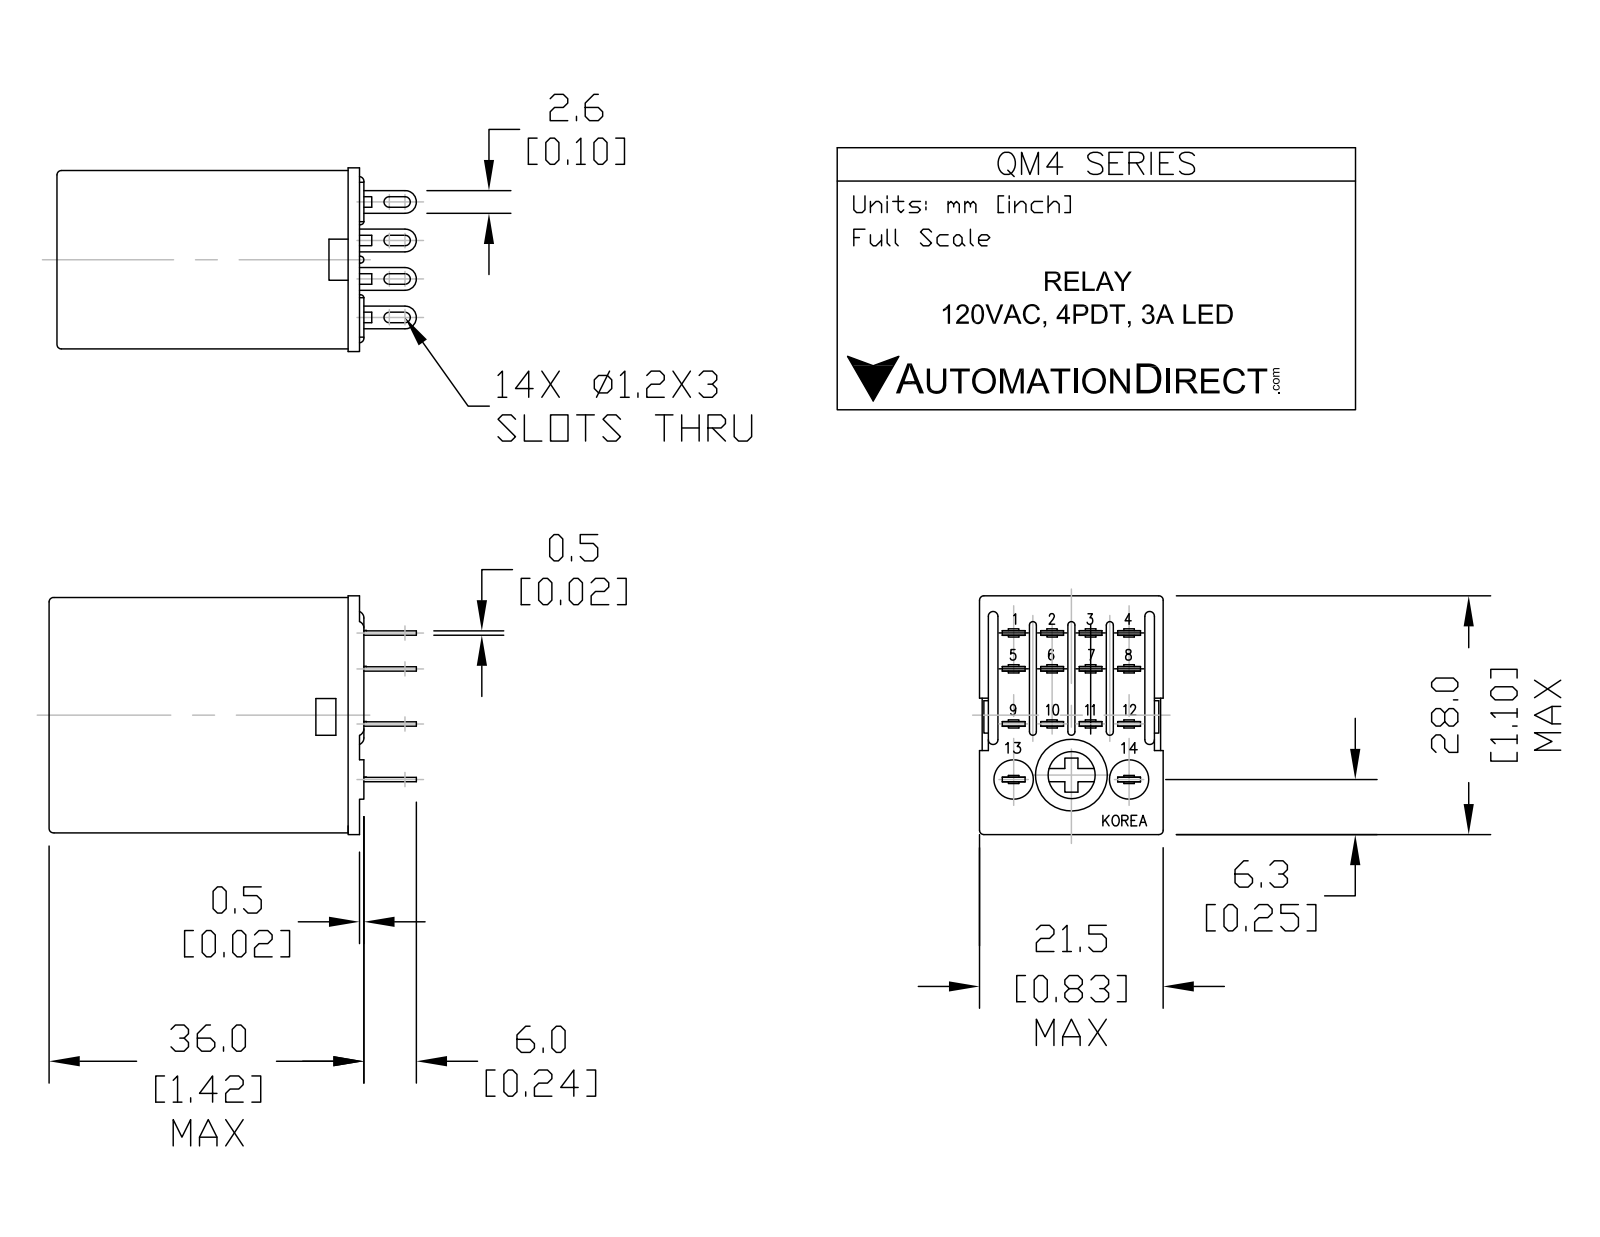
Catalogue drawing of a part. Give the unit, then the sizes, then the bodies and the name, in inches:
Units: inches
Overall size (bounding box): 1.654 × 1.102 × 0.846
Round holes (diameter × count): ⌀0.256 ×1
Round bosses / shafts (diameter × count): ⌀0.165 ×2, ⌀0.157 ×1
Partial cylindrical surfaces — rounded edges, fillets, slot ends (radius × count): R0.039 ×12, R0.02 ×8, R0.024 ×8
Main face-to-face distances: 1.398, 0.02, 0.256, 0.177, 0.433, 0.236, 0.276, 1.417, 0.059, 0.413
Volume: 1.177 in³ · Surface area: 7.792 in²
Bodies: 1 solid, 241 faces (161 planar, 76 cylindrical, 4 other)
Part name (STEP PRODUCT): QM4N1-A220
STEP written by: SolidWorks 2013 (AUTOMOTIVE_DESIGN)
